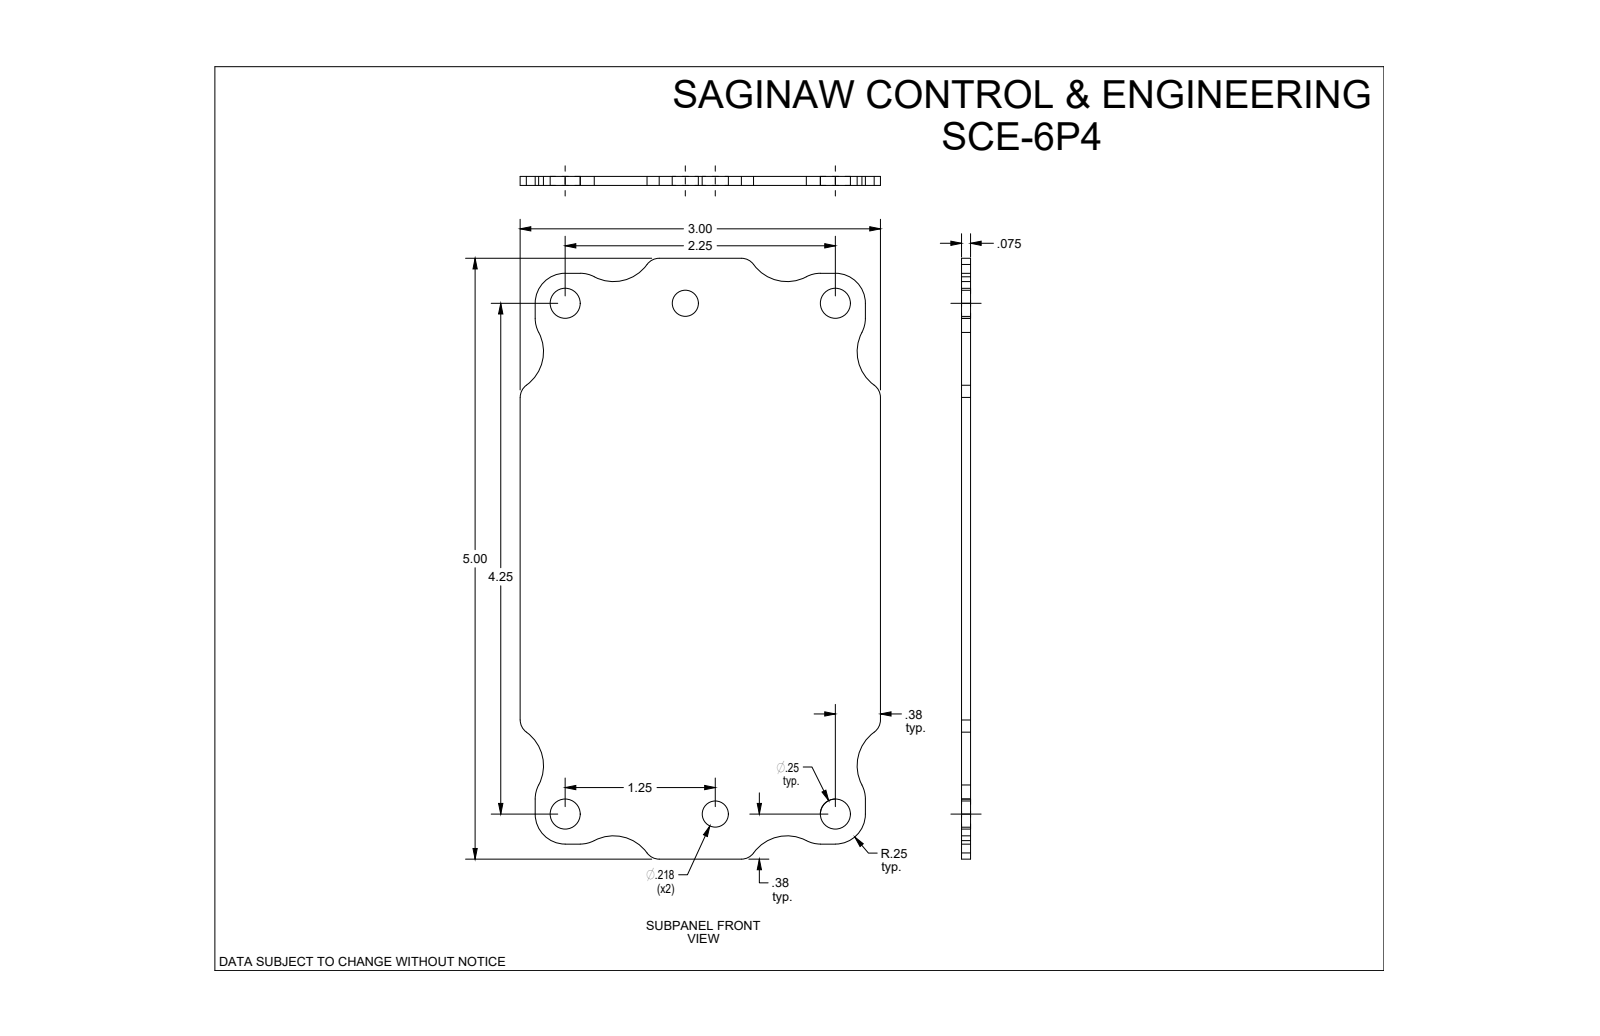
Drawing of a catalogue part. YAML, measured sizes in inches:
part_name: "SCE-6P4"
step_written_by: "SolidWorks 2019 (CONFIG_CONTROL_DESIGN)"
units: inches
bodies: {solids: 1, faces: 48, planar: 14, cylindrical: 34, other: 0}
overall_size: [5, 3, 0.075]
volume: 1.015
surface_area: 28.53
round_holes:
  - {diameter: 0.25, count: 4}
  - {diameter: 0.218, count: 2}
partial_cylinders:
  - {radius: 0.25, count: 12}
  - {radius: 0.125, count: 8}
  - {radius: 0.344, count: 8}
face_to_face_distances: [0.075, 3, 0.125, 5, 4.875, 2.875, 4.75, 2.75]
hole_center_spacings: [1, 1.25, 2.25, 4.25, 4.366, 4.43, 4.808, 4.257]
